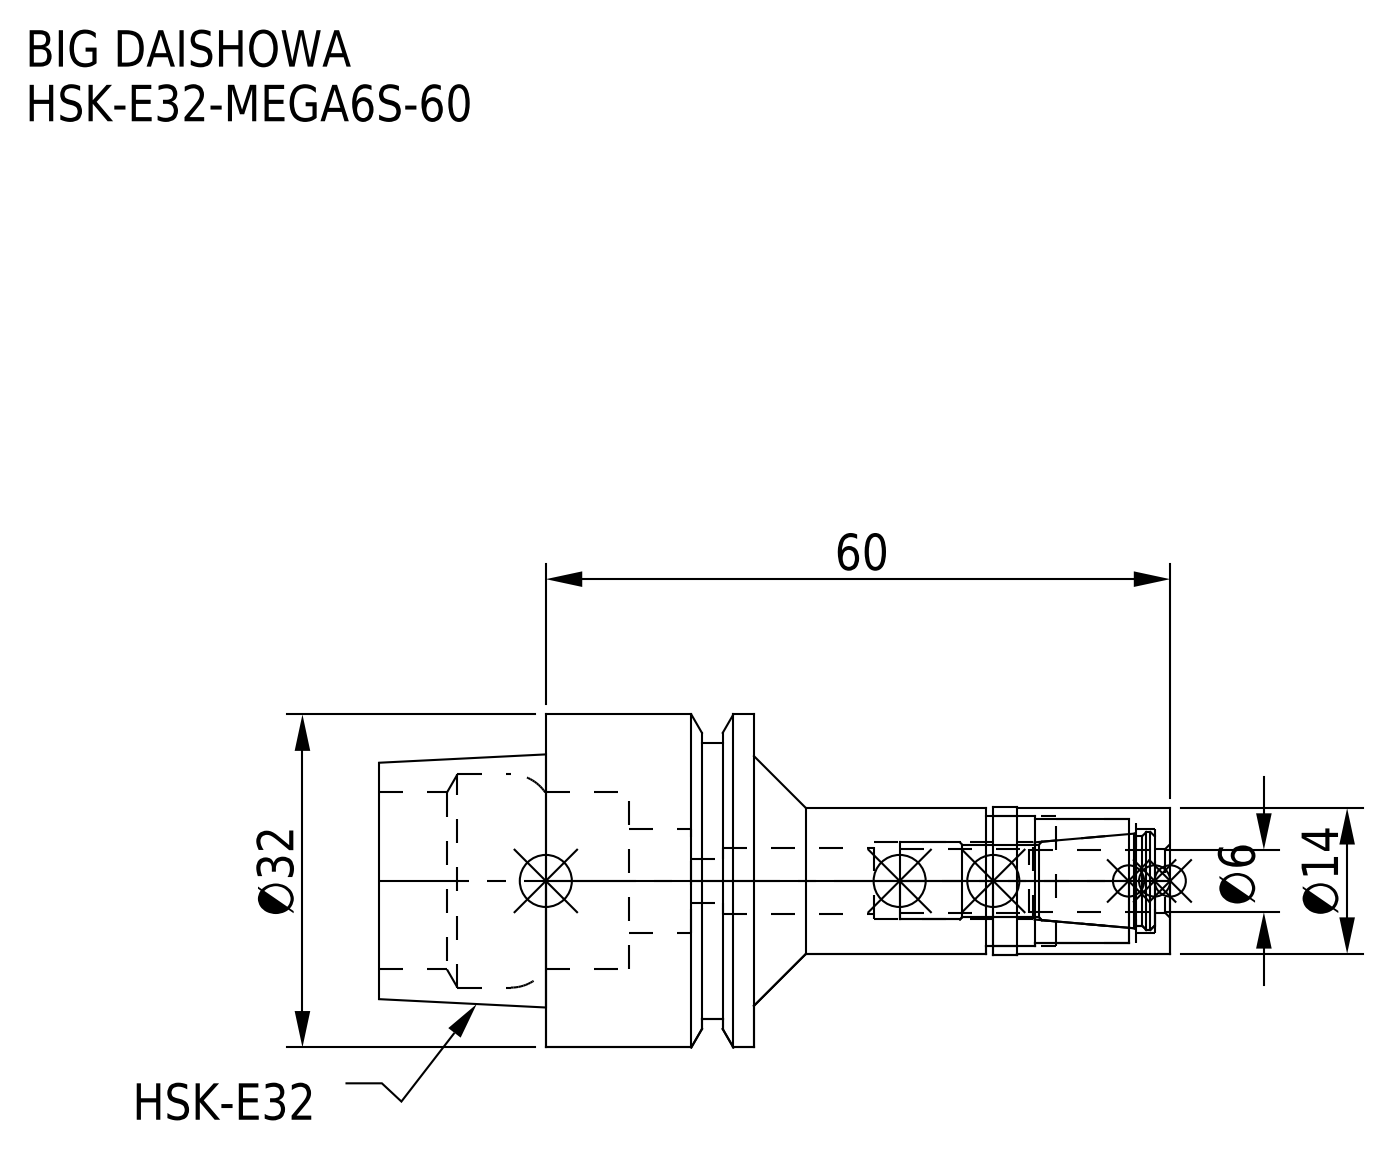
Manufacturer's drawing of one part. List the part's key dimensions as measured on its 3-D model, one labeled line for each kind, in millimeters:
Part name (STEP PRODUCT): MGN6S_1.stp; HSK-E32-MEGA6S-60; DXF_TEMP_ASSY_ASM_4_ASM.stp; HSK-E32-MEGA6S-60-060.stp (+3 more)
STEP written by: SolidWorks 2019 (CONFIG_CONTROL_DESIGN)
Units: millimetres
Bodies: 2 solids, 74 faces (18 planar, 40 cylindrical, 16 other)
Overall size (bounding box): 76 × 32 × 32
Volume: 20 529 mm³ · Surface area: 10 614 mm²
Round holes (diameter × count): ⌀4.2 ×1, ⌀6.1 ×1, ⌀6.4 ×1, ⌀7.4 ×1, ⌀10 ×1, ⌀12 ×1, ⌀12.5 ×1, ⌀17 ×1, ⌀20.5 ×1
Round bosses / shafts (diameter × count): ⌀32 ×1, ⌀26.5 ×1, ⌀14.3 ×1, ⌀14 ×1
Main face-to-face distances: 20, 36, 16, 12.05, 7.95, 23.95, 17, 43, 40, 52.05
